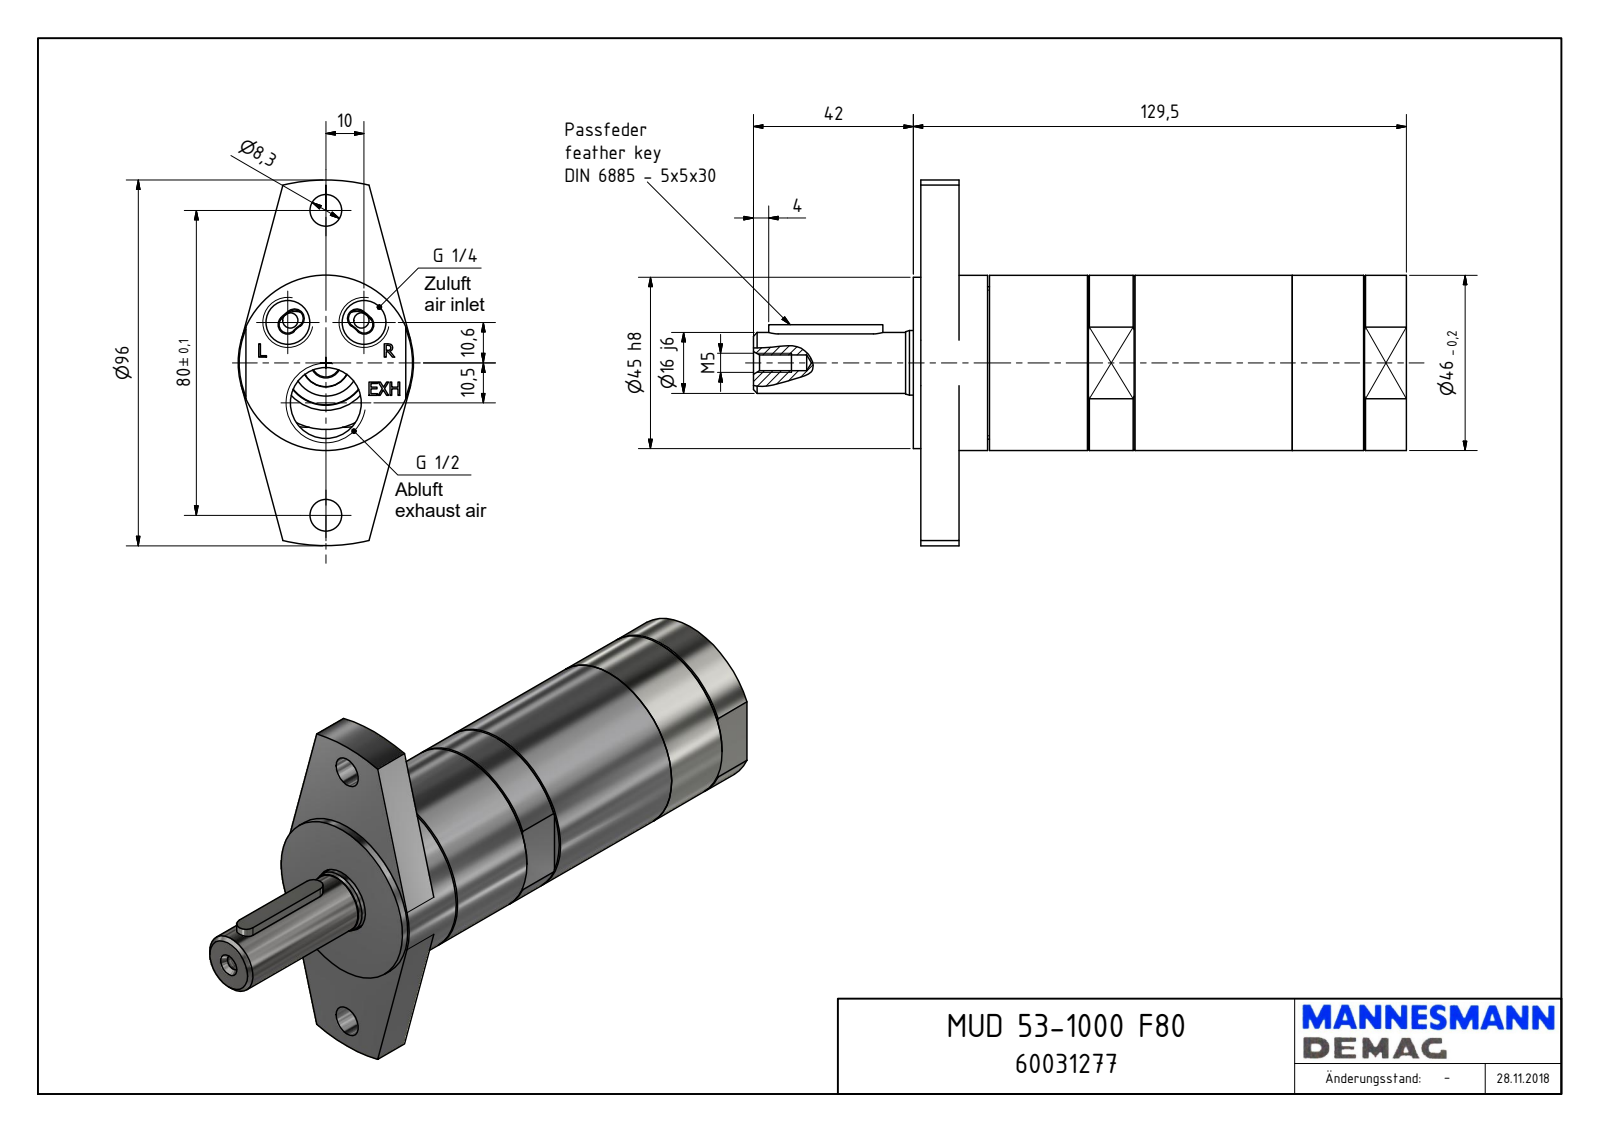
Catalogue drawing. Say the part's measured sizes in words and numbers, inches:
The part is named "MUD 53-1000 F80_60031277". Its 3-D file was written by "Autodesk Inventor 2018 (AUTOMOTIVE_DESIGN)". It is 1 solid with 164 faces: 99 planar, 34 cylindrical and 31 other. Overall it measures 6.752 by 3.78 by 1.811 inches. Its volume is 14.25 cubic inches and its surface area 51.27 square inches. Round holes: 2 of diameter 0.327, 2 of diameter 0.451, 1 of diameter 0.163, 1 of diameter 0.689, 1 of diameter 0.733, 1 of diameter 0.846, 1 of diameter 0.906. Round bosses or shafts: 1 of diameter 1.811, 1 of diameter 1.772, 1 of diameter 1.575, 1 of diameter 0.77, 1 of diameter 0.667, 1 of diameter 0.63. Partial cylindrical surfaces (rounded edges, fillets, slot ends): 2 of radius 0.098, 2 of radius 0.197, 1 of radius 0.716, 1 of radius 0.748, 1 of radius 1.89. The main face-to-face distances are 0.394, 0.472, 0.079, 5.098, 5.02, 4.626, 1.654, 1.811, 0.315, 4.311. The hole center spacings are 0.574, 0.919, 1.222, 1.575, 2.031, 0.413, 0.787, 1.161.
